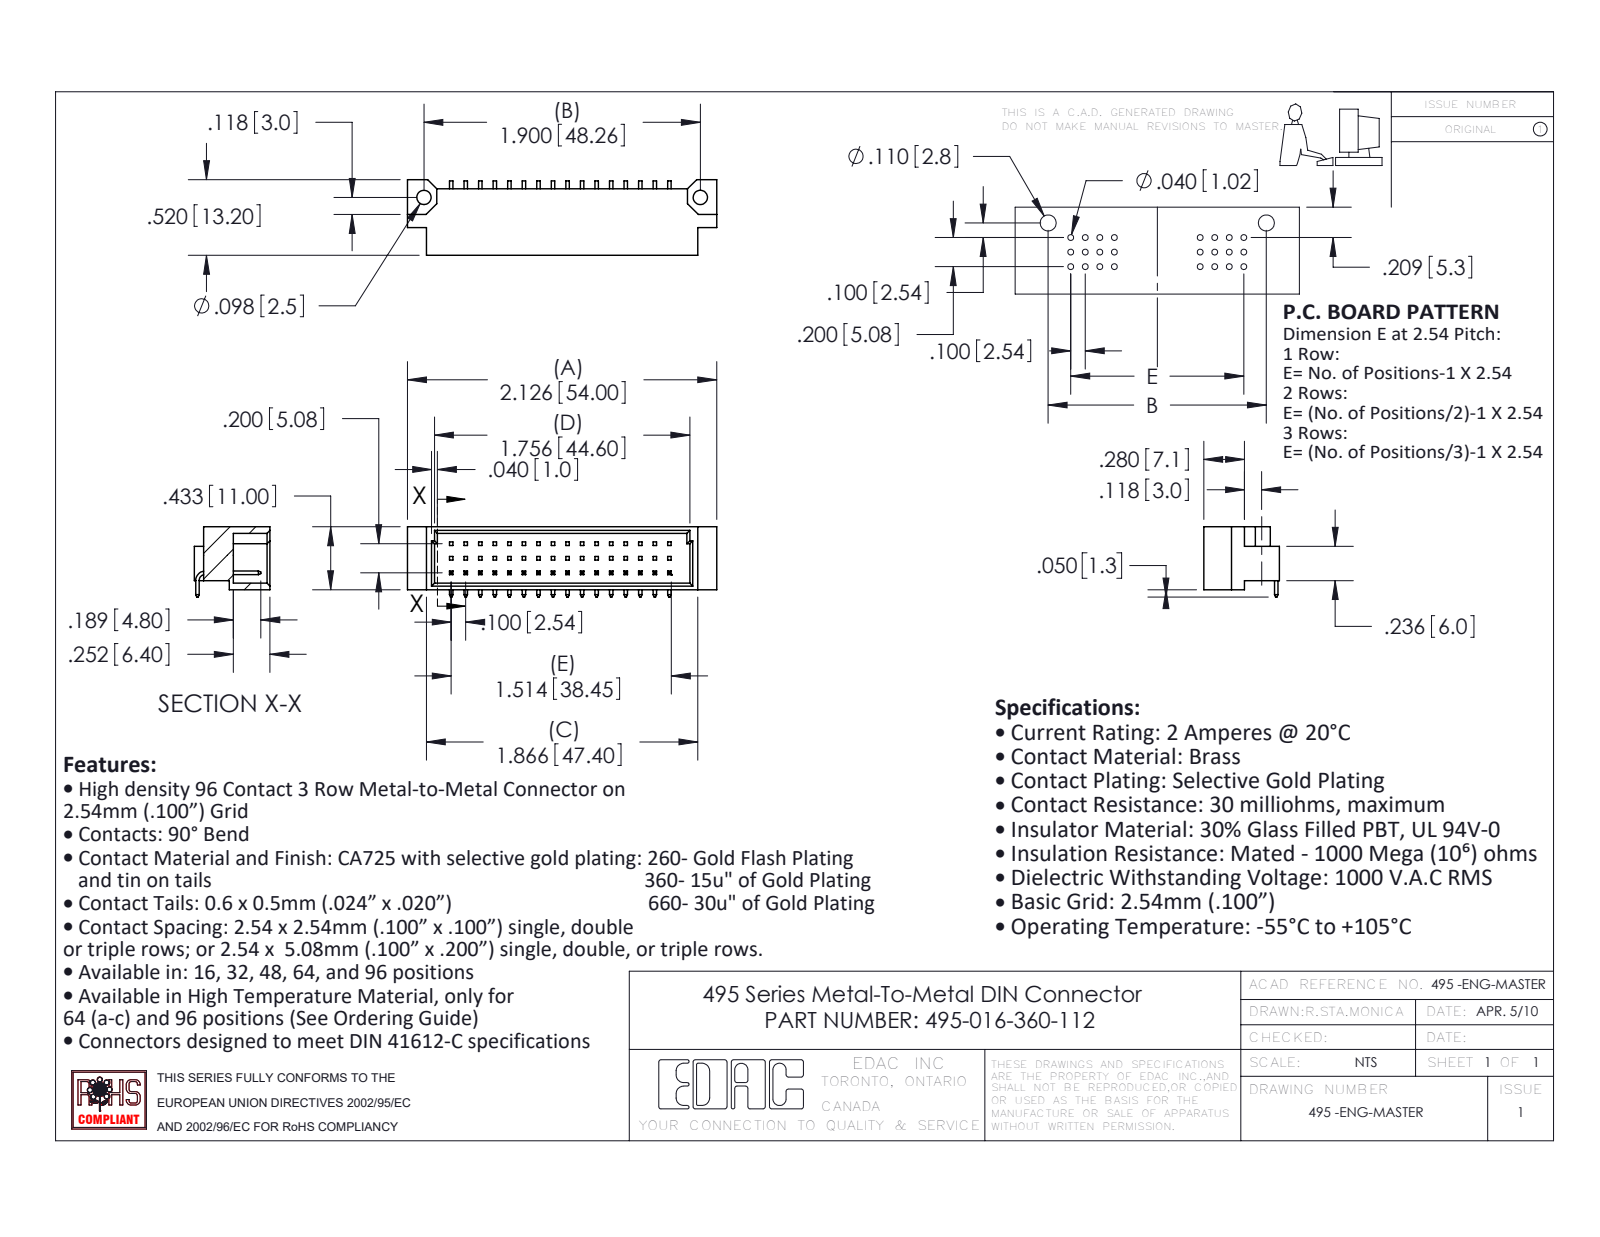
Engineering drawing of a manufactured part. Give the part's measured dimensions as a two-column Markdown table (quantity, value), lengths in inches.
| quantity | value |
| --- | --- |
| part name | 495 Part_48; 495-290-3; 495-016-360-112 |
| STEP written by | SolidWorks 2020 (AUTOMOTIVE_DESIGN) |
| units | inches |
| bodies | 17 solids, 530 faces (494 planar, 36 cylindrical, 0 other) |
| overall size | 2.126 × 0.52 × 0.483 |
| volume | 0.216 in³ |
| surface area | 7.023 in² |
| round holes (diameter × count) | 0.098 × 2 |
| partial cylindrical surfaces (radius × count) | 0.04 × 1, 0.065 × 1 |
| main face-to-face distances | 0.045, 0.388, 0.205, 0.1, 0.433, 0.063, 0.2, 0.024, 0.343, 0.37 |
| hole center spacings | 1.9 |
